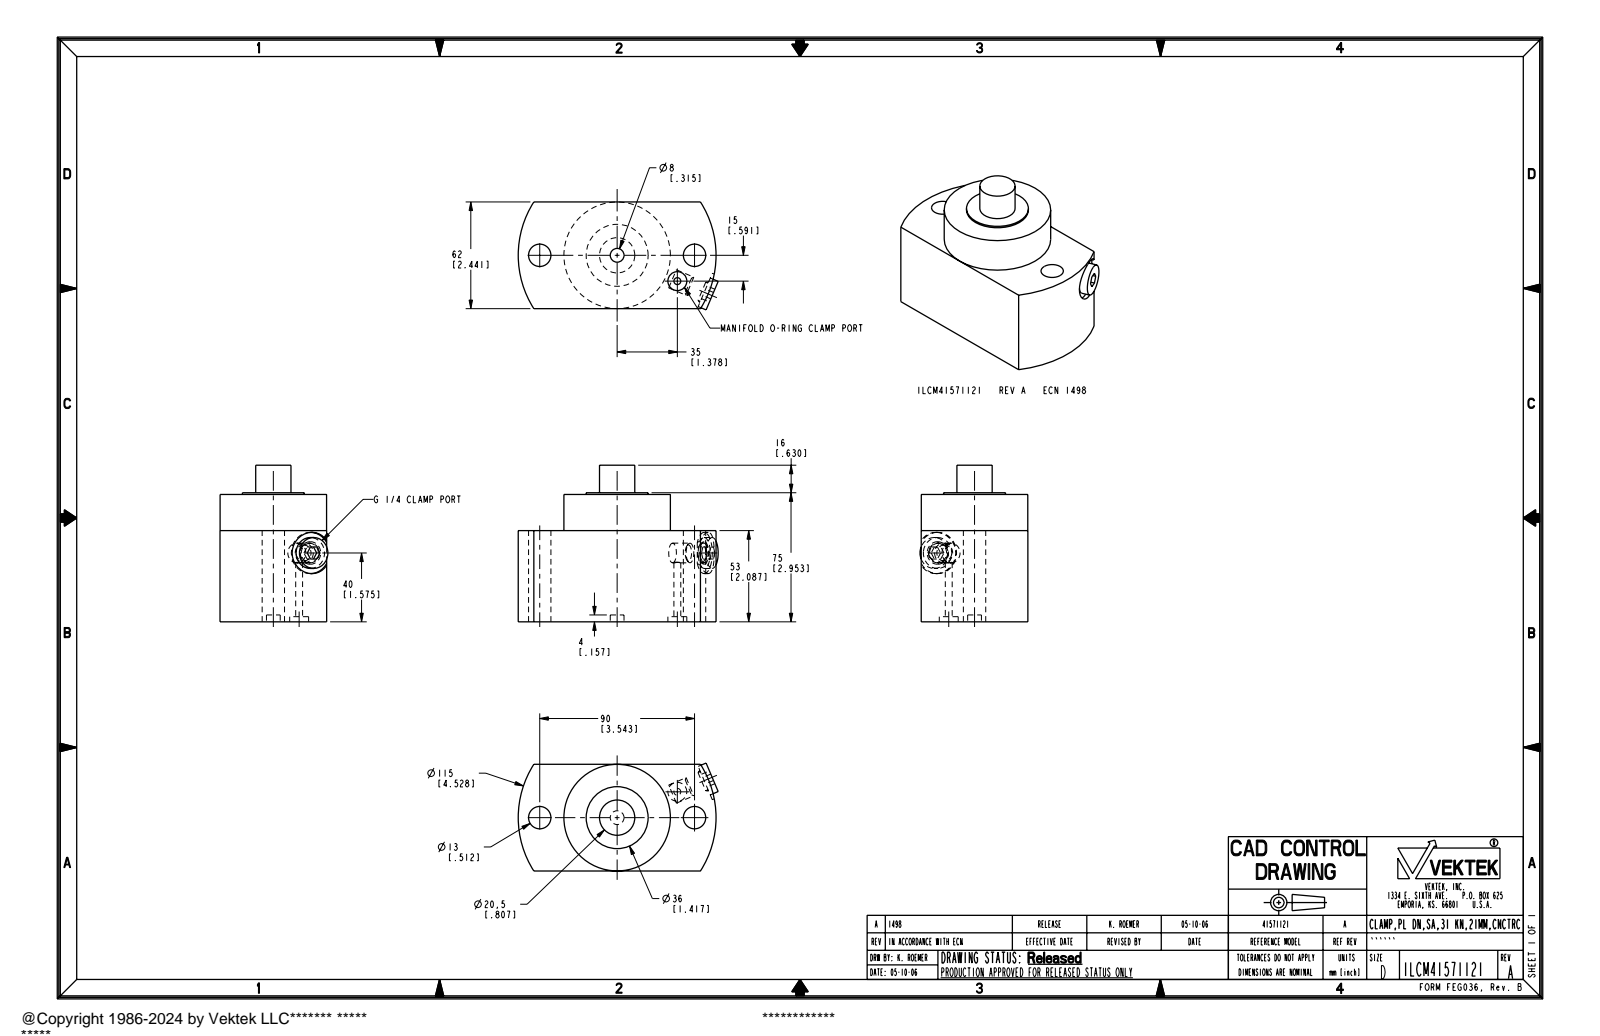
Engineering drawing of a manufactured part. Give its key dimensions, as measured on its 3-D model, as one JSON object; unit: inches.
{"part_name": "ILCM41571121", "step_written_by": "PRO/ENGINEER BY PARAMETRIC TECHNOLOGY CORPORATION, 2004290 (AUTOMOTIVE_DESIGN_CC2)", "units": "inches", "bodies": {"solids": 1, "faces": 52, "planar": 21, "cylindrical": 27, "other": 4}, "overall_size": [4.577, 3.583, 2.47], "volume_in3": 25.16, "surface_area_in2": 64.51, "round_holes": [[0.512, 2], [0.157, 1], [0.315, 1], [0.433, 1], [0.451, 1], [0.945, 1]], "round_bosses_or_shafts": [[2.437, 1], [1.417, 1], [0.807, 1], [0.709, 1], [0.451, 1]], "partial_cylinders_radius": [[2.264, 1]], "face_to_face_distances": [2.441, 2.087, 2.913, 0.827, 0.039, 2.953, 0.866, 3.583, 1.496, 0.669], "hole_center_spacings": [1.772, 0.71, 1.499, 3.204, 3.543]}
